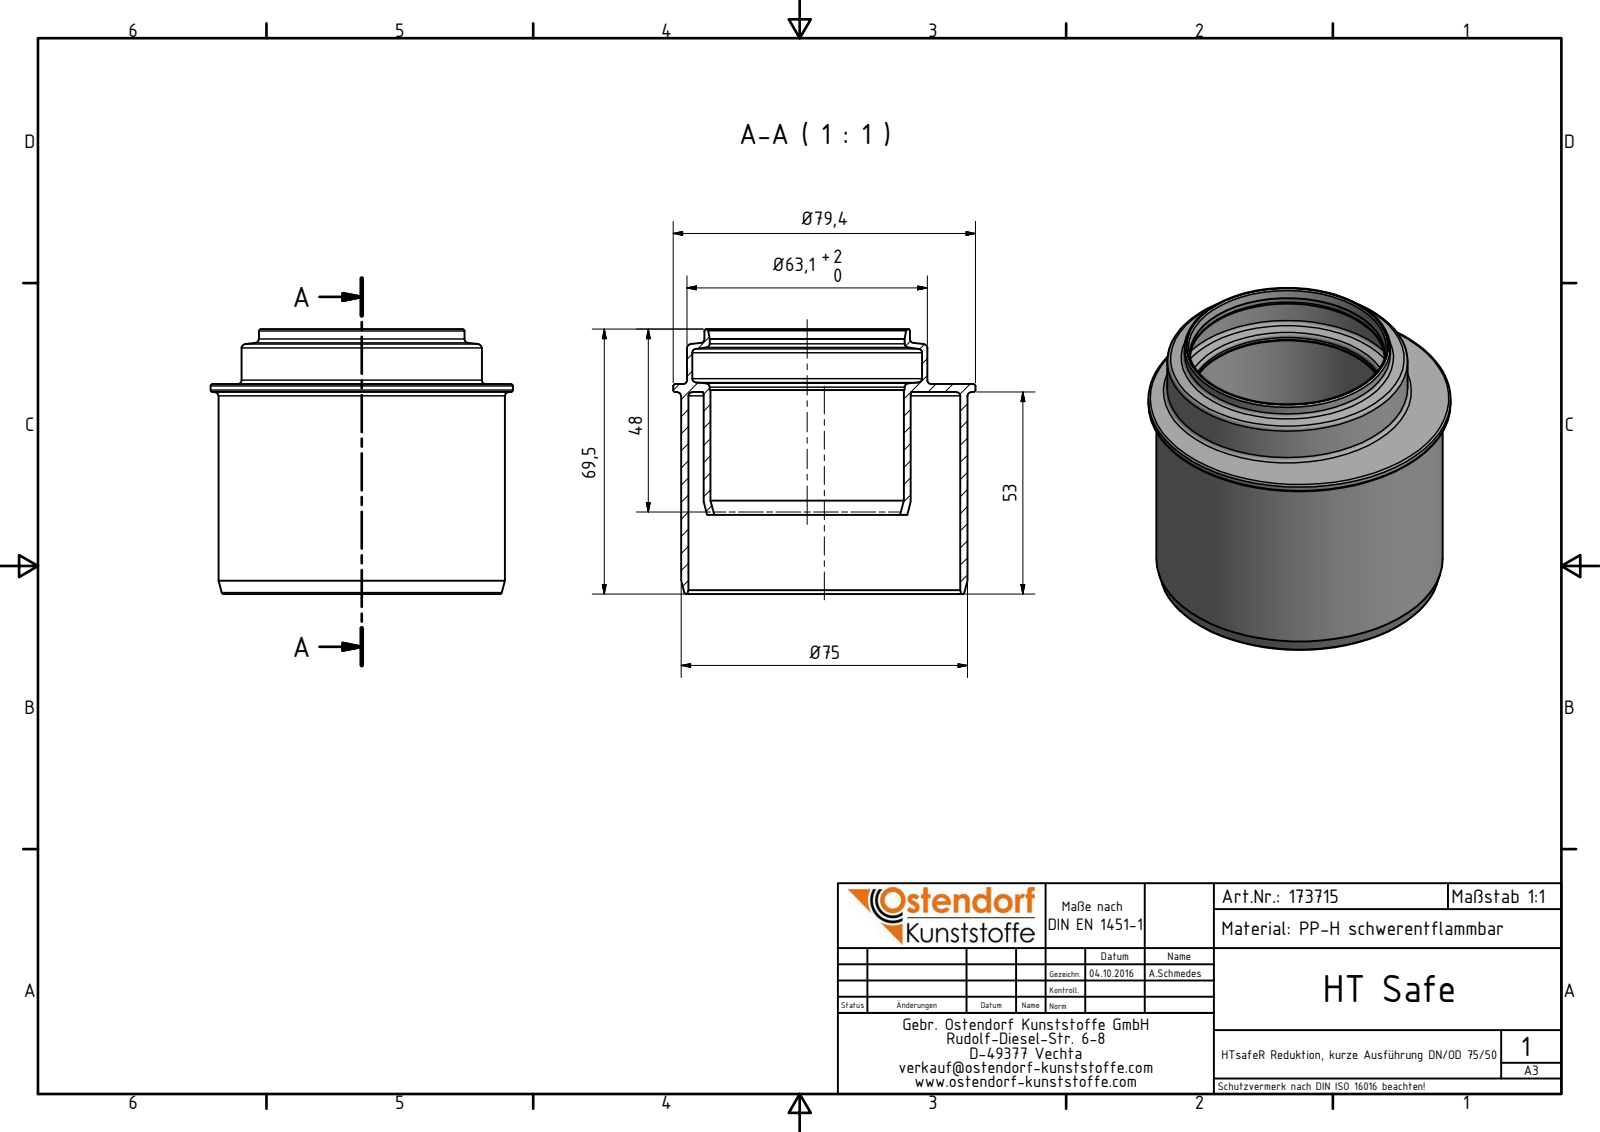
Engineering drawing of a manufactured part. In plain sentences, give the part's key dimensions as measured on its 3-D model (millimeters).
The part is named "173715 HTsafeR Reduktion,kurze Ausführung DN_OD 75_50". Its 3-D file was written by "Autodesk Inventor 2016 (AUTOMOTIVE_DESIGN)". It is 1 solid with 40 faces: 7 planar, 10 cylindrical and 23 other. Overall it measures 79.4 by 79.4 by 69.5 millimeters. Its volume is 43 464 cubic millimeters and its surface area 47 292 square millimeters. Round holes: 1 of diameter 50.8, 1 of diameter 51.2, 1 of diameter 60.3, 1 of diameter 71.4. Round bosses or shafts: 1 of diameter 79.4, 1 of diameter 75.2, 1 of diameter 63.1, 1 of diameter 54.4, 1 of diameter 54. The main face-to-face distances are 2.1, 32.24, 34.34, 20.76, 53, 55.1, 53.5, 32.74, 0.5, 1.6. The hole center spacings are 4.5.
